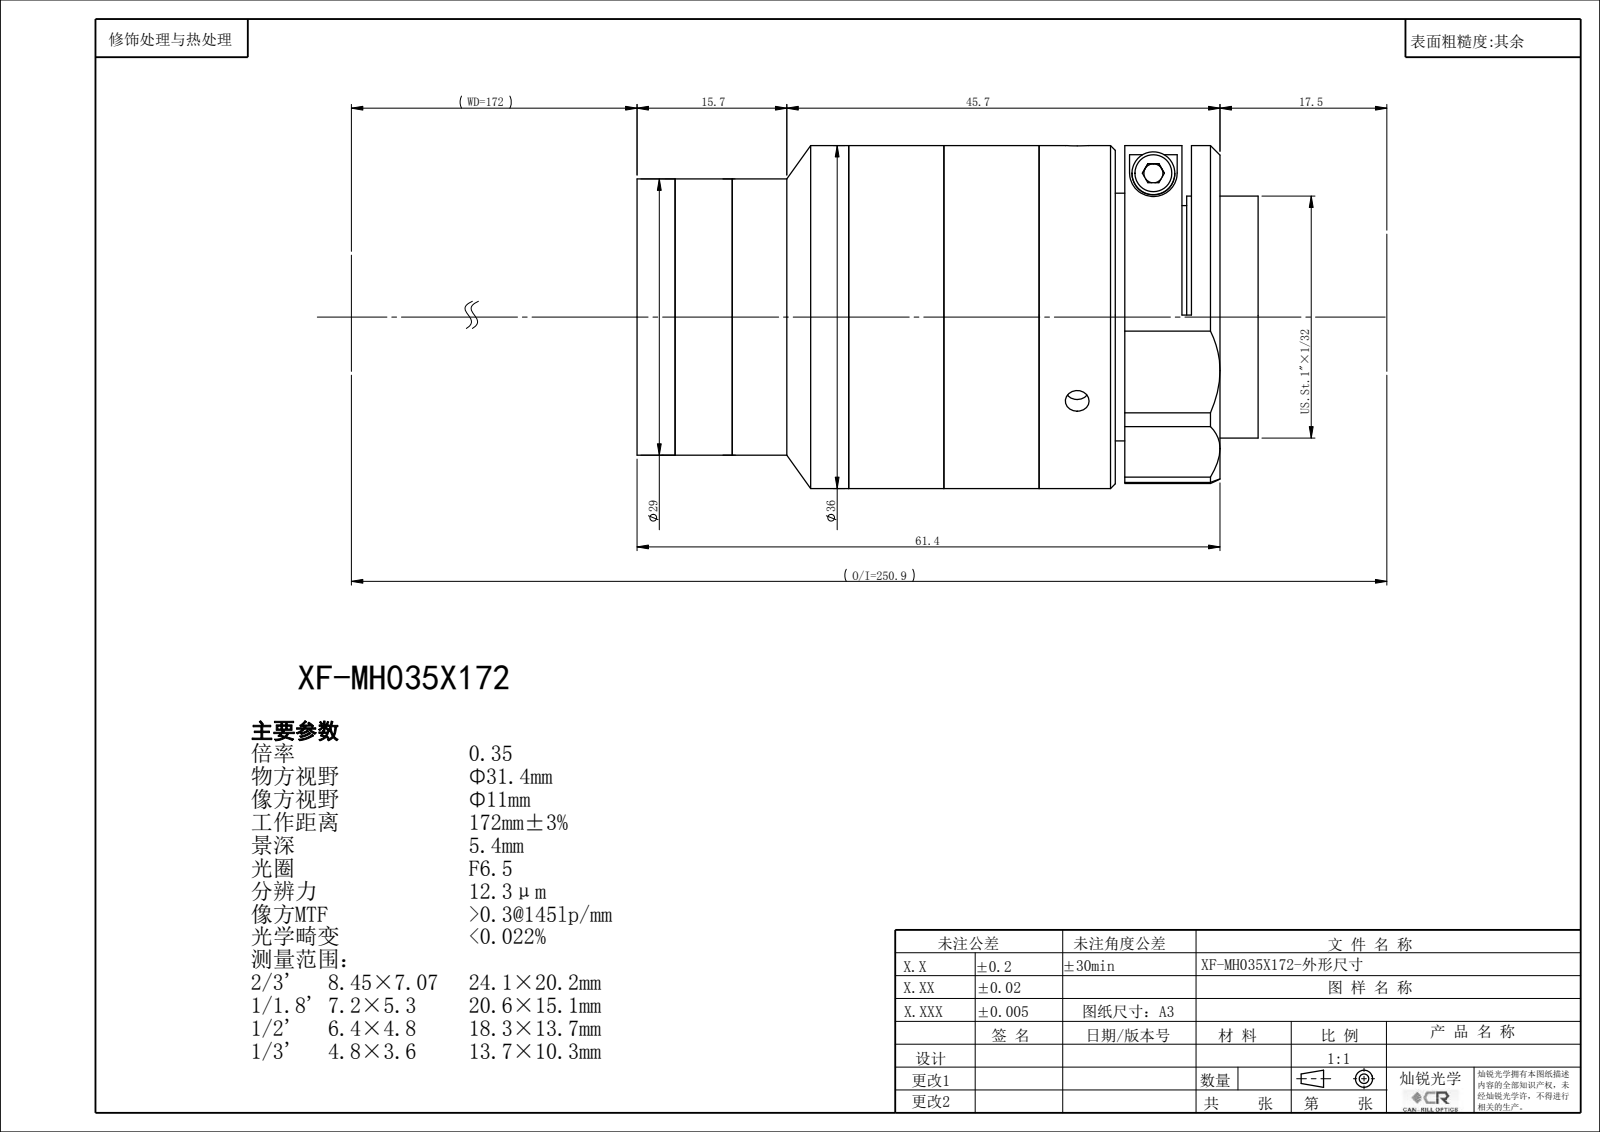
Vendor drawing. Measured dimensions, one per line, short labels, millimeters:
name: XF-MH035X172
written by: SolidWorks 2022 (CONFIG_CONTROL_DESIGN)
unit: mm
bodies: 21 solids, 361 faces (147 planar, 144 cylindrical, 70 other)
size: 65.48 × 36.01 × 36
volume: 37 948 mm³; area: 30 550 mm²
holes: 6× ⌀2.5, 1× ⌀7.18, 1× ⌀12, 1× ⌀14, 1× ⌀16.4, 1× ⌀18, 1× ⌀22.4, 1× ⌀24, 1× ⌀24.9, 1× ⌀26, 1× ⌀26.4, 1× ⌀27
bosses: 6× ⌀3, 1× ⌀36, 1× ⌀34, 1× ⌀32, 1× ⌀30, 1× ⌀29, 1× ⌀28, 1× ⌀25.4
face distances: 10, 3.5, 6.5, 4.5, 5.5, 1, 10.5, 16.5, 20, 32.24
hole spacings: 9.5
